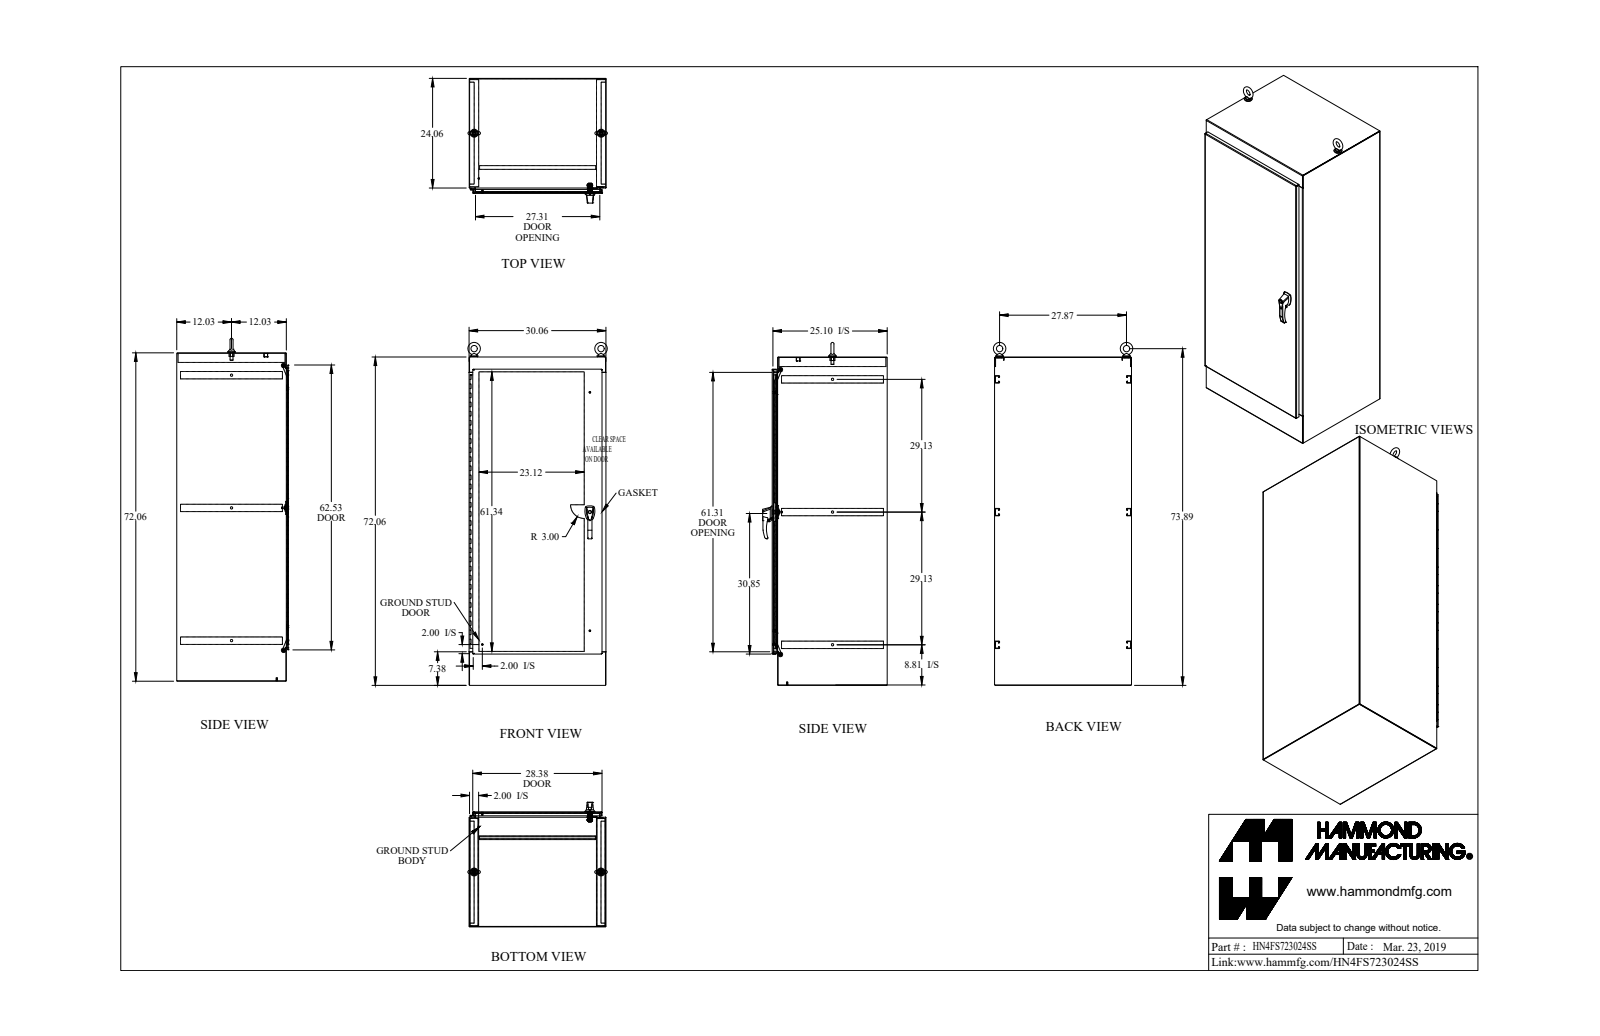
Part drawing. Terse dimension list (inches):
name: HN4FS723024SS
written by: SolidWorks 2018 (AUTOMOTIVE_DESIGN)
unit: in
bodies: 52 solids, 1857 faces (854 planar, 838 cylindrical, 165 other)
size: 75.256 × 30.604 × 27.362
volume: 1 067 in³; area: 22 394 in²
holes: 10× ⌀0.304, 7× ⌀0.35, 3× ⌀0.5, 2× ⌀0.25, 2× ⌀0.257, 2× ⌀0.28, 2× ⌀0.281, 2× ⌀0.313, 2× ⌀0.39, 2× ⌀0.413, 2× ⌀0.527, 2× ⌀0.625
bosses: 2× ⌀1.75, 2× ⌀1.5, 2× ⌀1.25, 2× ⌀1, 2× ⌀0.75, 2× ⌀0.738, 2× ⌀0.63, 2× ⌀0.625
rounds: 42× R0.043, 36× R0.138, 23× R0.5, 22× R0.125, 16× R0.018, 15× R0.048, 15× R0.06, 15× R0.143
face distances: 0.095, 25.152, 29.965, 29.87, 25.057, 25.247, 30.06, 71.965, 1.187, 23.965
hole spacings: 6, 12, 18, 24, 30, 36, 42, 0.015
